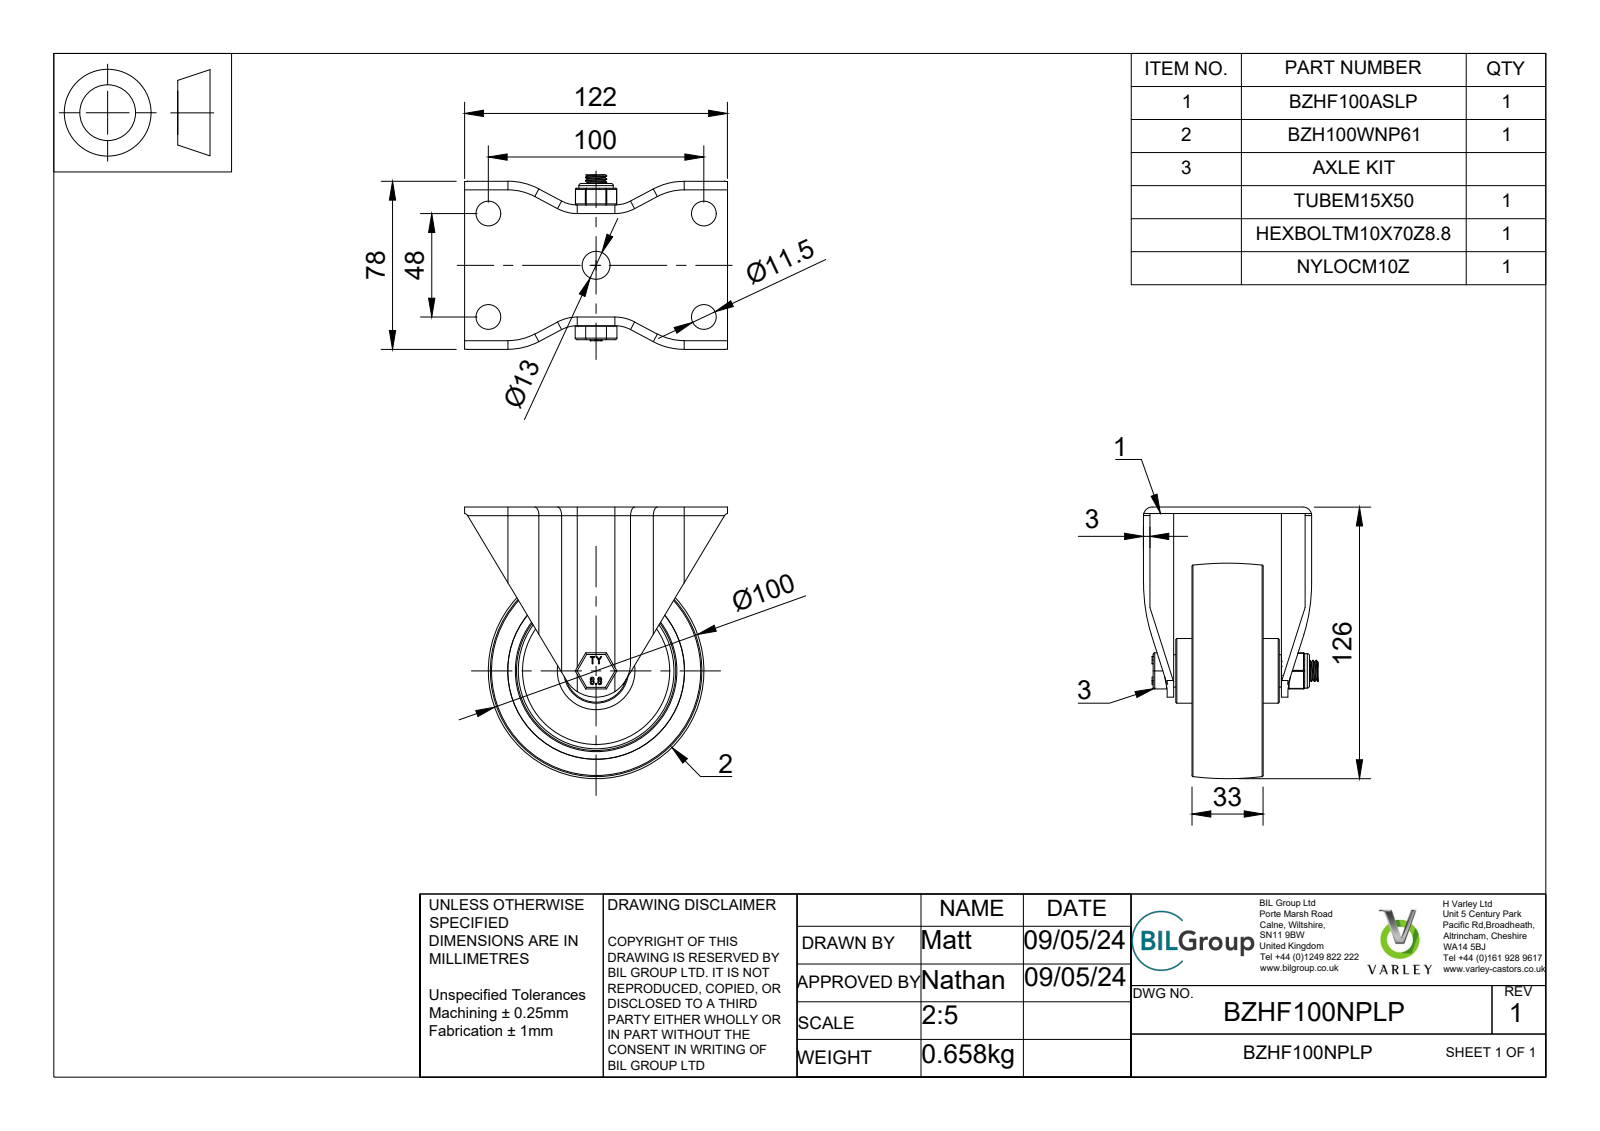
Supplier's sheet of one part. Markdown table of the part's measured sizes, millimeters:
| quantity | value |
| --- | --- |
| part name | BZHF100NPLP v3; BZHF100ASLP - 50 v1; ZINC PLATED PRESSED STEEL BRACKET; BZH100WNP61 v1 (+8 more) |
| STEP written by | Autodesk Translation Framework v12.20.1.177 (AUTOMOTIVE_DESIGN) |
| units | millimeters |
| bodies | 7 solids, 293 faces (110 planar, 111 cylindrical, 72 other) |
| overall size | 126 × 122 × 81 |
| volume | 232 387 mm³ |
| surface area | 105 027 mm² |
| round holes (diameter × count) | 11.5 × 4, 10 × 1, 10.5 × 1, 10.8 × 1, 12 × 1, 13 × 1, 15.4 × 1, 82 × 1 |
| round bosses / shafts (diameter × count) | 30 × 1, 16 × 1, 15 × 1, 9.85 × 1, 8.14 × 1 |
| partial cylindrical surfaces (radius × count) | 0.5 × 18, 4 × 8, 0.75 × 6, 15.5 × 4, 30.5 × 4, 2 × 2, 16 × 1 |
| main face-to-face distances | 3, 14, 22.5, 41.5, 19, 8.5, 27.5, 11, 64, 34.66 |
| hole center spacings | 55.46, 48, 100, 110.92 |
